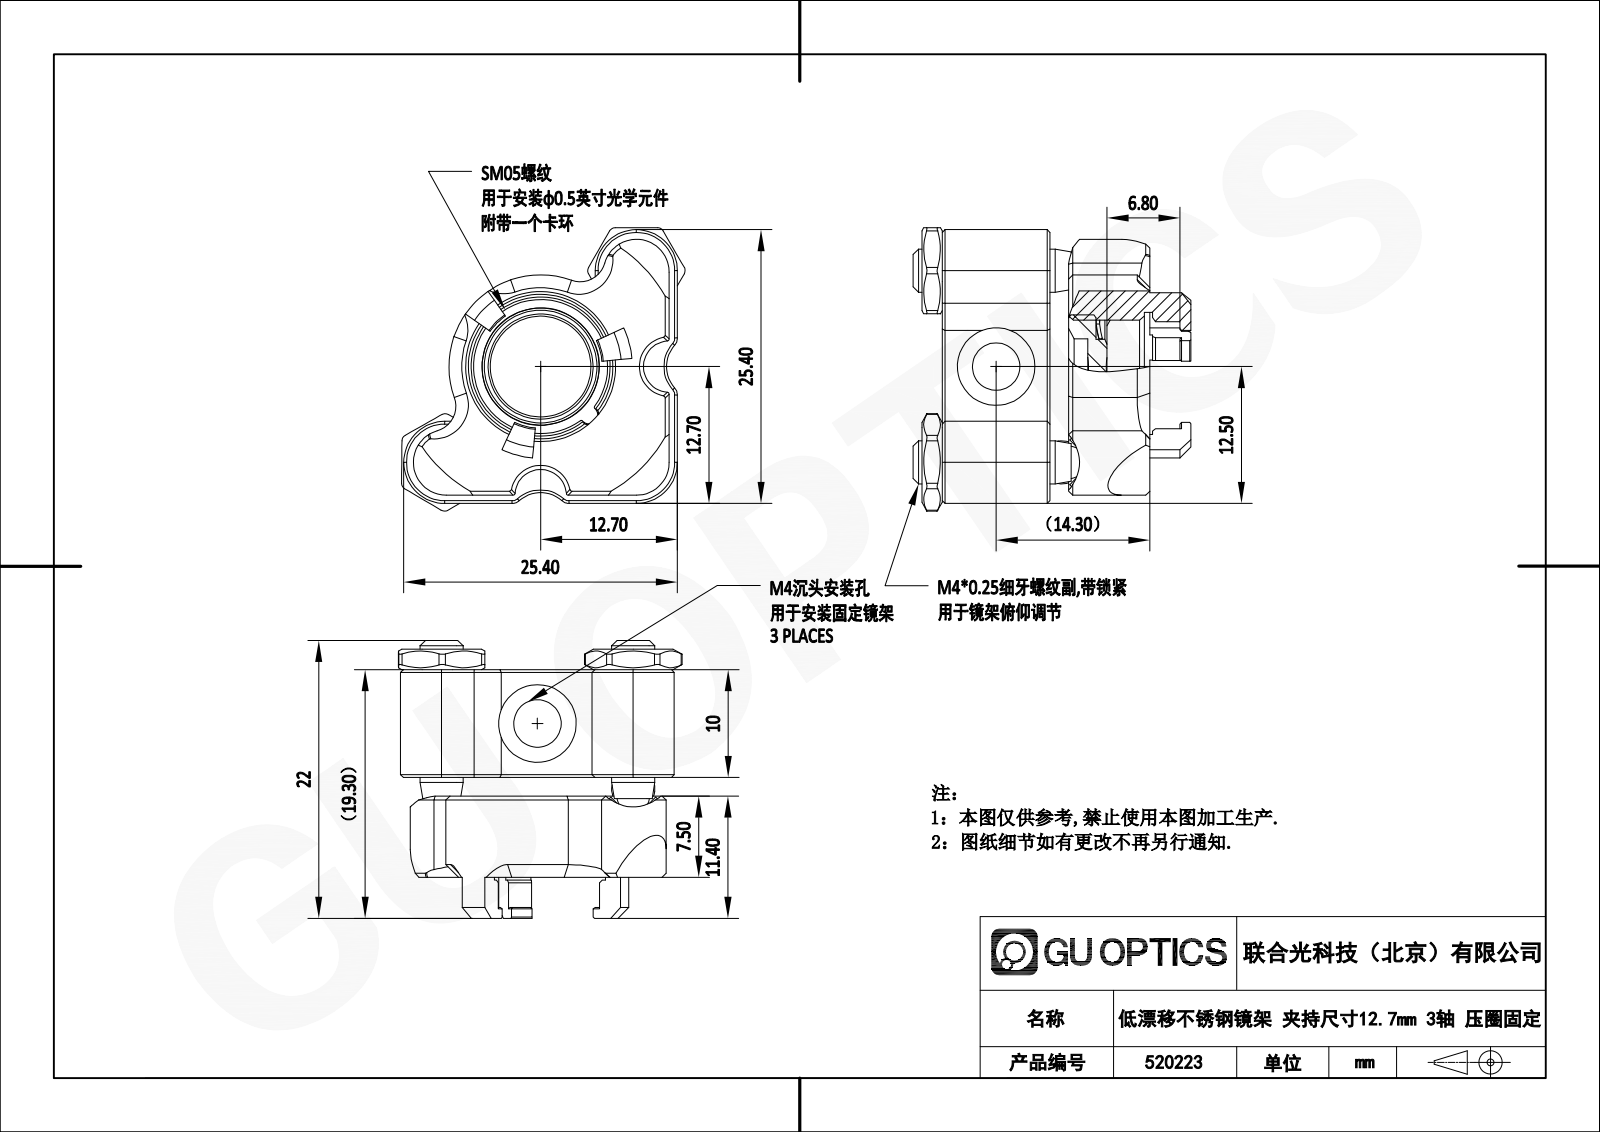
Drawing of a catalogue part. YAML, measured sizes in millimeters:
part_name: "1.1.20.25_ZJO-PSM0.5-3; ZFK不锈钢透镜卡环压圈_1.8.9.1_ZFKS-K05; 32.5.1-6，蓝宝石垫片，A; 1.1.20.24.1_替代进口不锈钢光学调整架前面板，低变形，SM0.5，含两个卡环，两轴 (+4 more)"
step_written_by: "SolidWorks 2021 (CONFIG_CONTROL_DESIGN)"
units: millimeters
bodies: {solids: 20, faces: 583, planar: 193, cylindrical: 171, other: 219}
overall_size: [26.33, 26.31, 26.14]
volume: 4487
surface_area: 5871
round_holes:
  - {diameter: 3.4, count: 5}
  - {diameter: 1.6, count: 4}
  - {diameter: 2.99, count: 3}
  - {diameter: 3.75, count: 3}
  - {diameter: 4, count: 3}
  - {diameter: 4.35, count: 3}
  - {diameter: 2, count: 2}
  - {diameter: 4.4, count: 2}
  - {diameter: 7.2, count: 2}
  - {diameter: 11.19, count: 1}
  - {diameter: 12.9, count: 1}
  - {diameter: 13.92, count: 1}
round_bosses_or_shafts:
  - {diameter: 2.5, count: 6}
  - {diameter: 2, count: 2}
  - {diameter: 13.59, count: 1}
partial_cylinders:
  - {radius: 0.6, count: 18}
  - {radius: 1, count: 8}
  - {radius: 3.05, count: 3}
  - {radius: 3.81, count: 3}
  - {radius: 0.19, count: 2}
  - {radius: 0.19, count: 2}
  - {radius: 2.38, count: 2}
  - {radius: 2.39, count: 2}
face_to_face_distances: [2, 10, 9.54, 19.54, 12, 7.54, 1.9, 0.76, 0.77, 8]
hole_center_spacings: [9.72, 11.74, 12.83, 4.95, 4.96, 7.87, 12.57, 18.46]
